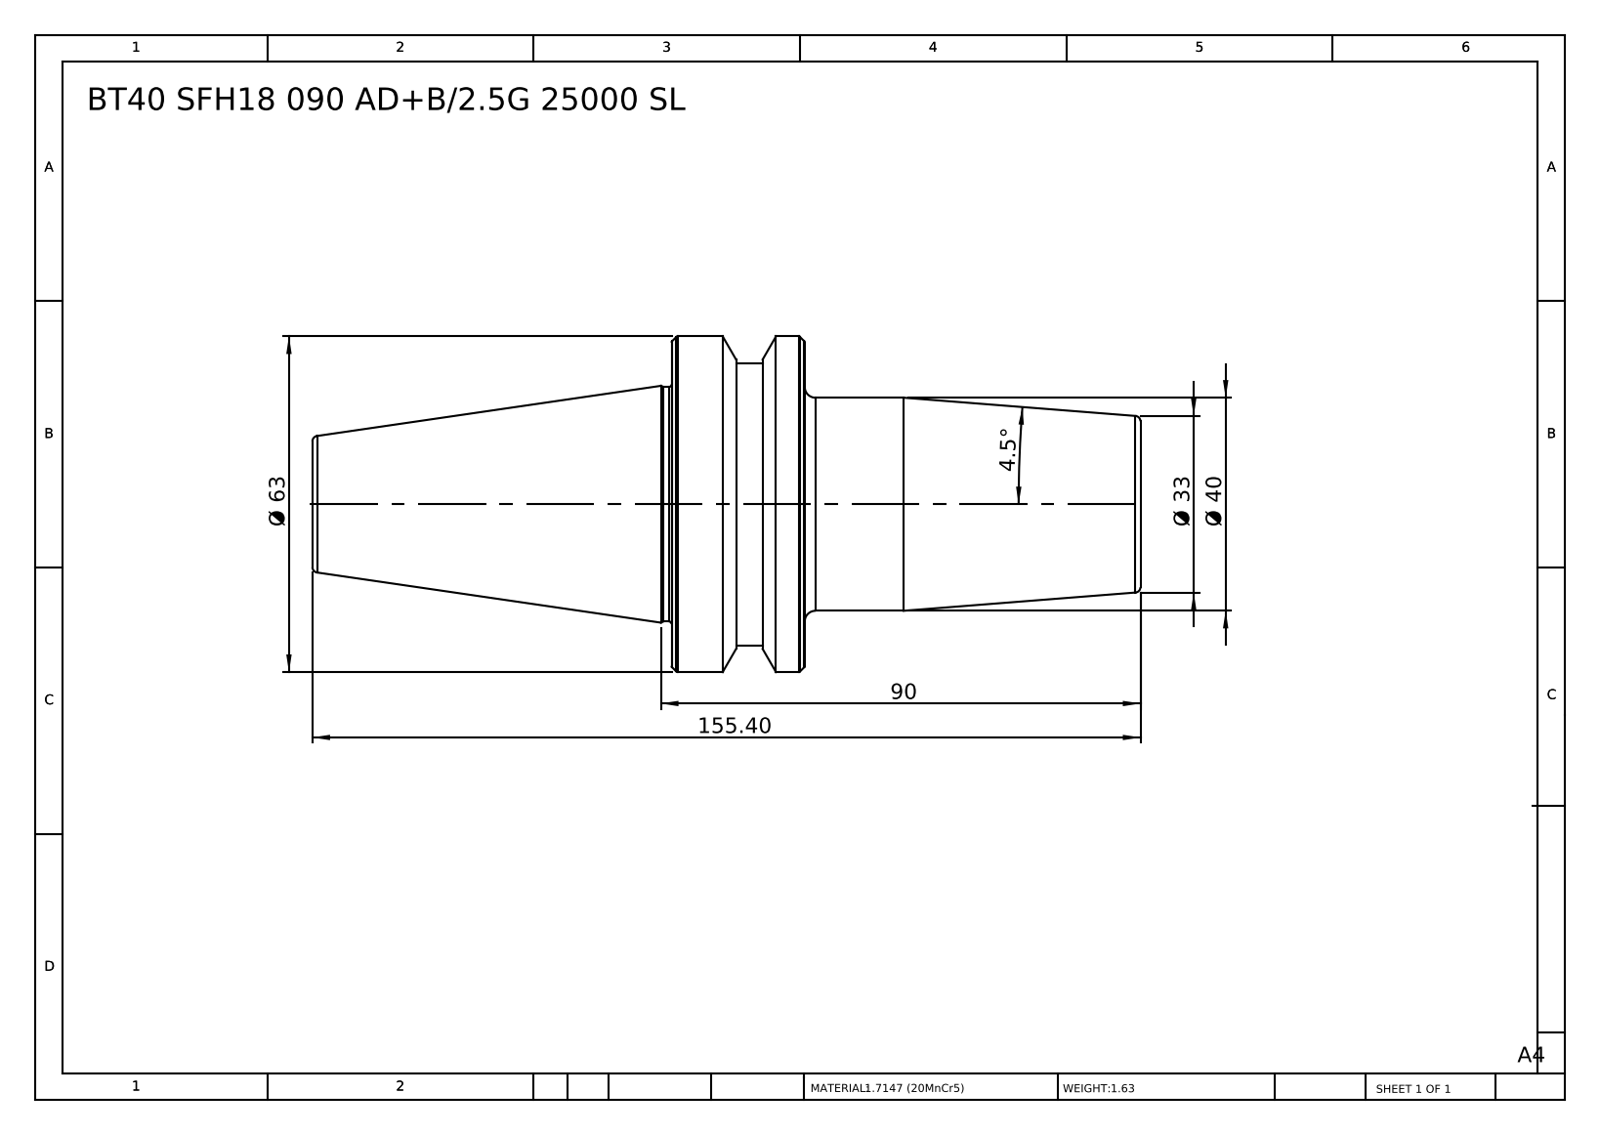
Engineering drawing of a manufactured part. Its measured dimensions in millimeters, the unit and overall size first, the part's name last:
Units: millimetres
Overall size (bounding box): 155.4 × 63 × 63
Round bosses / shafts (diameter × count): ⌀63 ×1, ⌀53 ×1, ⌀44 ×1, ⌀40 ×1
Main face-to-face distances: 25, 63, 88, 155.4, 92.4, 67.4, 70.9, 7.9, 17.1, 84.5
Volume: 208 393 mm³ · Surface area: 25 219 mm²
Bodies: 1 solid, 46 faces (6 planar, 10 cylindrical, 30 other)
Part name (STEP PRODUCT): BT40 SFH18 090 AD+B-2.5G 25000 SL
STEP written by: SolidWorks 2014 (CONFIG_CONTROL_DESIGN)
